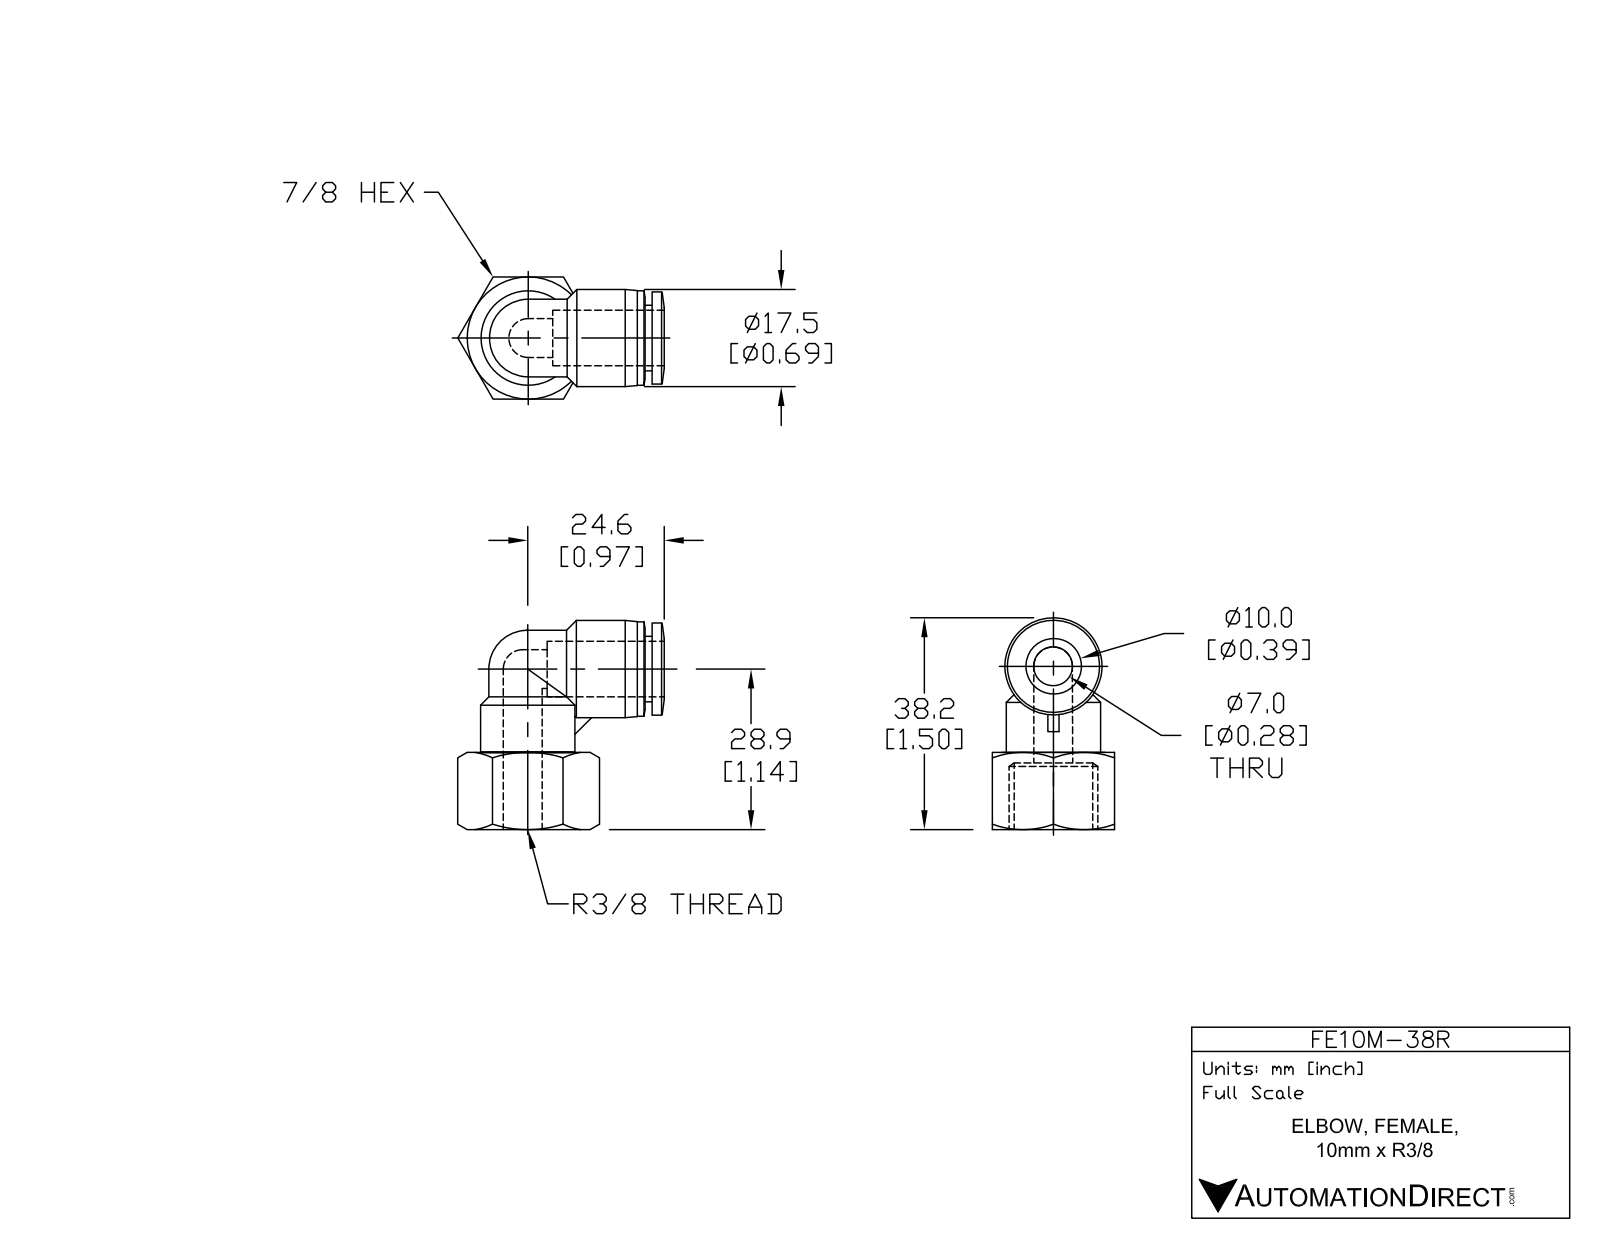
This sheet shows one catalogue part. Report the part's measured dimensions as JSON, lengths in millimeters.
{"part_name": "FE10M-38R", "step_written_by": "SolidWorks 2015 (AUTOMOTIVE_DESIGN)", "units": "millimeters", "bodies": {"solids": 1, "faces": 70, "planar": 17, "cylindrical": 20, "other": 33}, "overall_size": [38.3, 37.3, 22], "volume_mm3": 8780, "surface_area_mm2": 5694, "round_holes": [[7, 2], [10.3, 1]], "round_bosses_or_shafts": [[17, 2], [17.5, 1], [16.6, 1], [14, 1], [11.8, 1]], "partial_cylinders_radius": [[7, 1]], "face_to_face_distances": [22, 12, 2, 14, 1.2, 16.7, 18, 10, 15.3, 1.4]}
